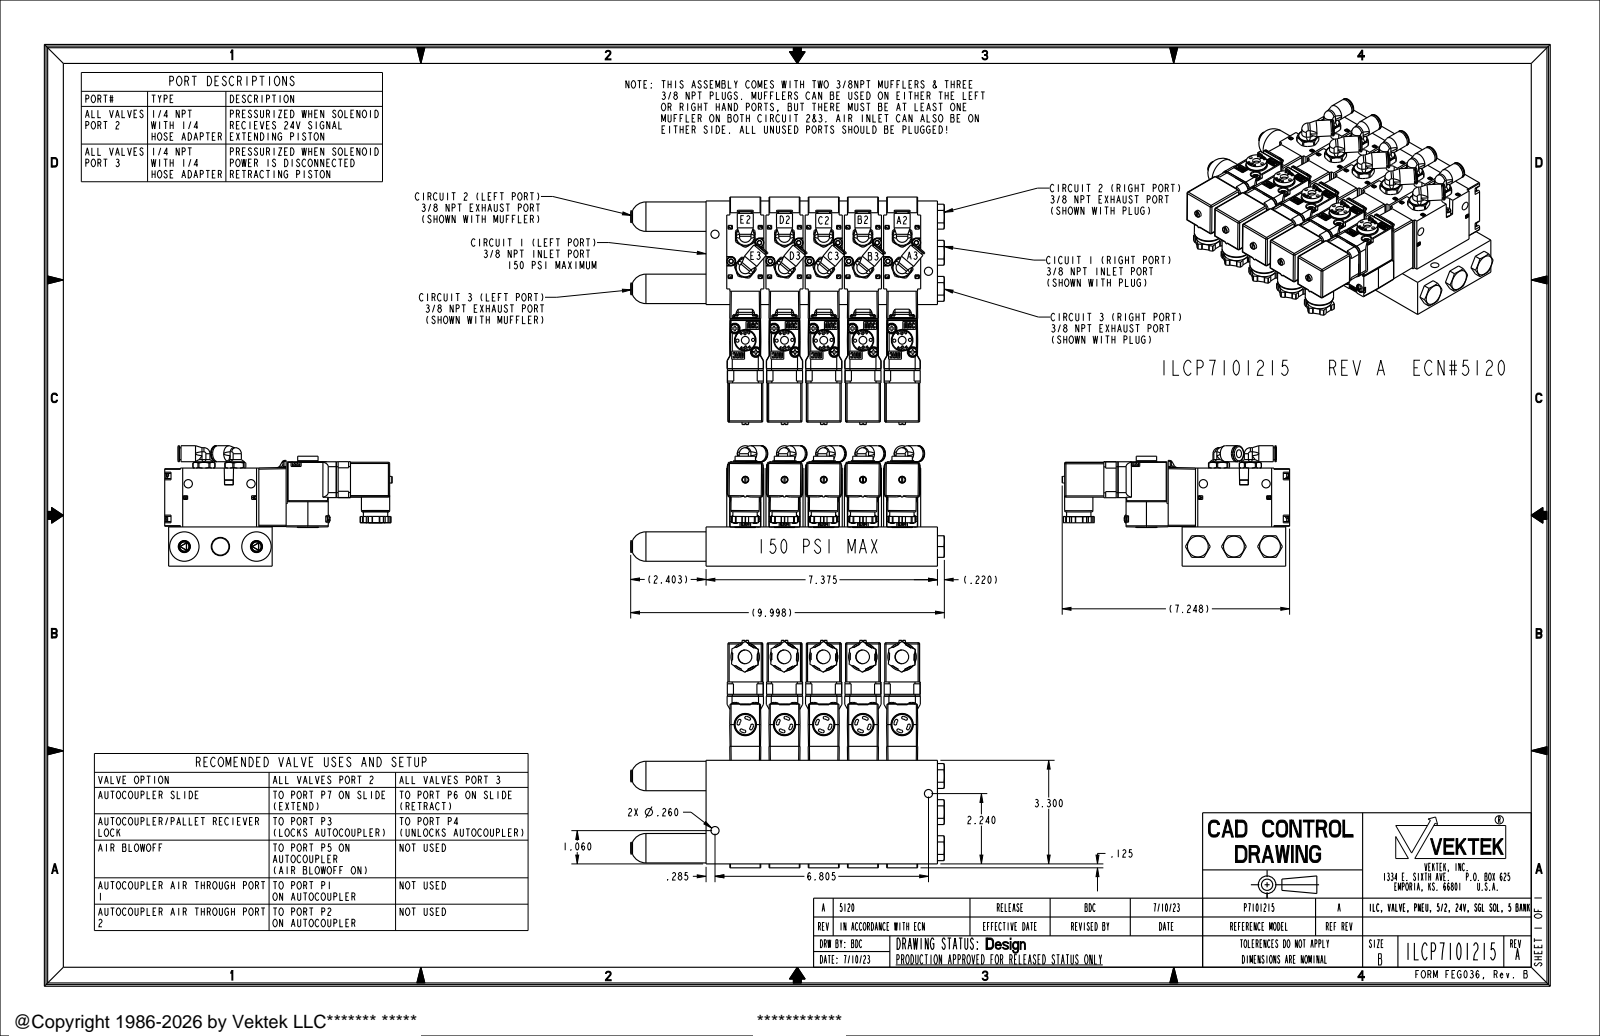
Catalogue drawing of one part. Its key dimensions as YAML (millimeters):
part_name: "ILCP7101215"
step_written_by: "CREO PARAMETRIC BY PTC INC, 2021164 (AUTOMOTIVE_DESIGN)"
units: millimeters
bodies: {solids: 6, faces: 6651, planar: 3612, cylindrical: 1578, other: 1461}
overall_size: [253.9, 184.1, 97.5]
volume: 1645000
surface_area: 266900
round_holes:
  - {diameter: 3.5, count: 20}
  - {diameter: 6.4, count: 20}
  - {diameter: 2.5, count: 10}
  - {diameter: 2.8, count: 10}
  - {diameter: 3.2, count: 10}
  - {diameter: 6.5, count: 10}
  - {diameter: 7.3, count: 10}
  - {diameter: 2.7, count: 5}
  - {diameter: 2.8, count: 5}
  - {diameter: 6, count: 5}
  - {diameter: 6.3, count: 5}
  - {diameter: 11.1, count: 5}
round_bosses_or_shafts:
  - {diameter: 7, count: 30}
  - {diameter: 6.5, count: 20}
  - {diameter: 9.5, count: 12}
  - {diameter: 16.5, count: 10}
  - {diameter: 14.8, count: 10}
  - {diameter: 13, count: 10}
  - {diameter: 6.8, count: 10}
  - {diameter: 22.9, count: 5}
partial_cylinders:
  - {radius: 0.2, count: 120}
  - {radius: 1, count: 100}
  - {radius: 0.3, count: 70}
  - {radius: 0.5, count: 61}
  - {radius: 4, count: 60}
  - {radius: 0.8, count: 53}
  - {radius: 0.9, count: 40}
  - {radius: 1.1, count: 40}
face_to_face_distances: [31.8, 63.5, 95.3, 30, 127, 61.7, 1.8, 33.5, 93.5, 79.4]
hole_center_spacings: [31.8, 63.5, 95.3, 127, 53.4, 25.4, 40.7, 57.9]
